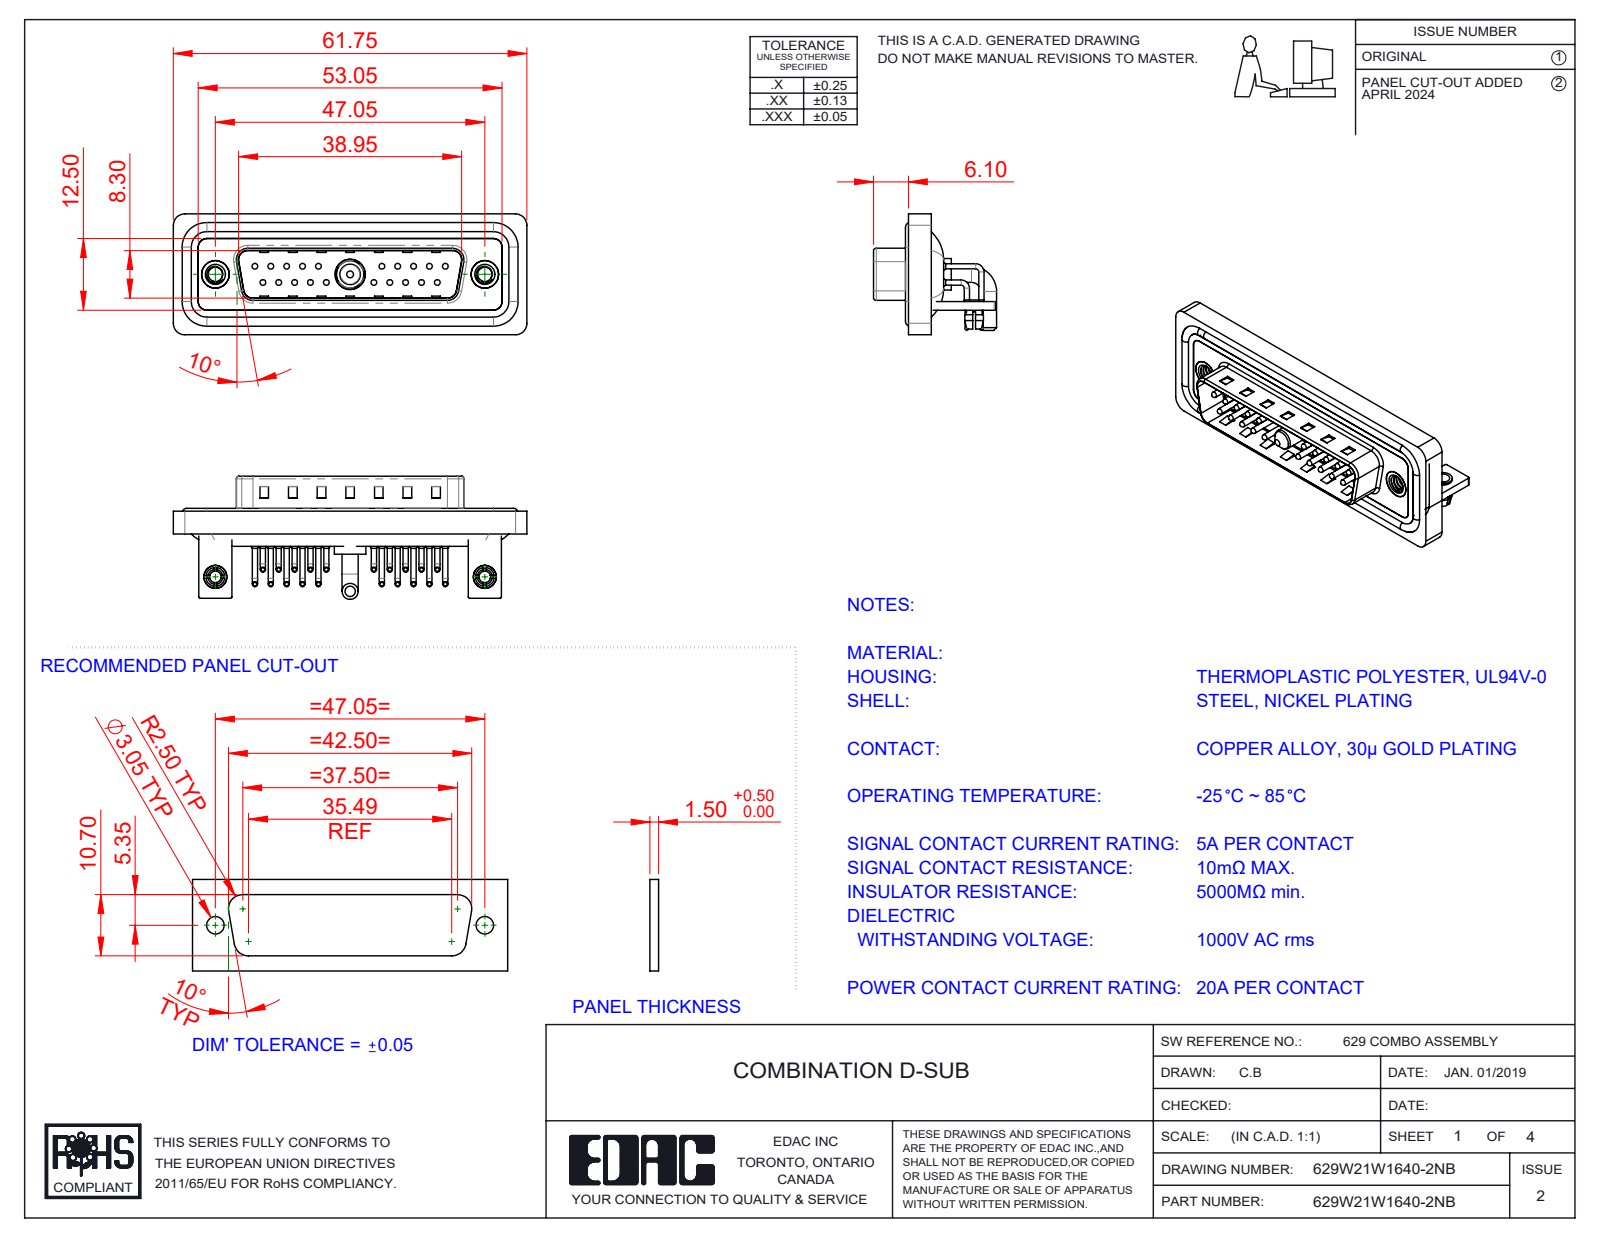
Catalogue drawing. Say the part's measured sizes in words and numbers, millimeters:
The part is named "629Combo Shell Rear_25 Contacts; 629Combo Stabilizer Bracket; 629Combo Threaded Rivet_B; Power Pin_20A RA (+7 more)". Its 3-D file was written by "SolidWorks 2023 (CONFIG_CONTROL_DESIGN)". It is 33 solids with 2856 faces: 1567 planar, 979 cylindrical and 310 other. Overall it measures 61.75 by 21.5 by 21.1 millimeters. Its volume is 7 726 cubic millimeters and its surface area 13 519 square millimeters. Round holes: 22 of diameter 2, 20 of diameter 0.75, 20 of diameter 1.6, 4 of diameter 2.5, 2 of diameter 3.2, 2 of diameter 4, 2 of diameter 4.8, 2 of diameter 5, 1 of diameter 4.85, 1 of diameter 5.3. Round bosses or shafts: 40 of diameter 0.9, 20 of diameter 1.5, 20 of diameter 1, 20 of diameter 0.65, 4 of diameter 1.6, 2 of diameter 4.9, 2 of diameter 4, 2 of diameter 3.4. Partial cylindrical surfaces (rounded edges, fillets, slot ends): 20 of radius 1.01, 19 of radius 2, 18 of radius 1.5, 16 of radius 0.25, 9 of radius 0.5, 8 of radius 1.6, 4 of radius 0.6, 4 of radius 0.65. The main face-to-face distances are 0.4, 0.8, 2.1, 2.9, 1.5, 1.1, 4.1, 1.6, 4.5, 3.7. The hole center spacings are 3.16, 2.77, 5.54, 8.31, 5.04, 19.39, 20.97, 22.16.
